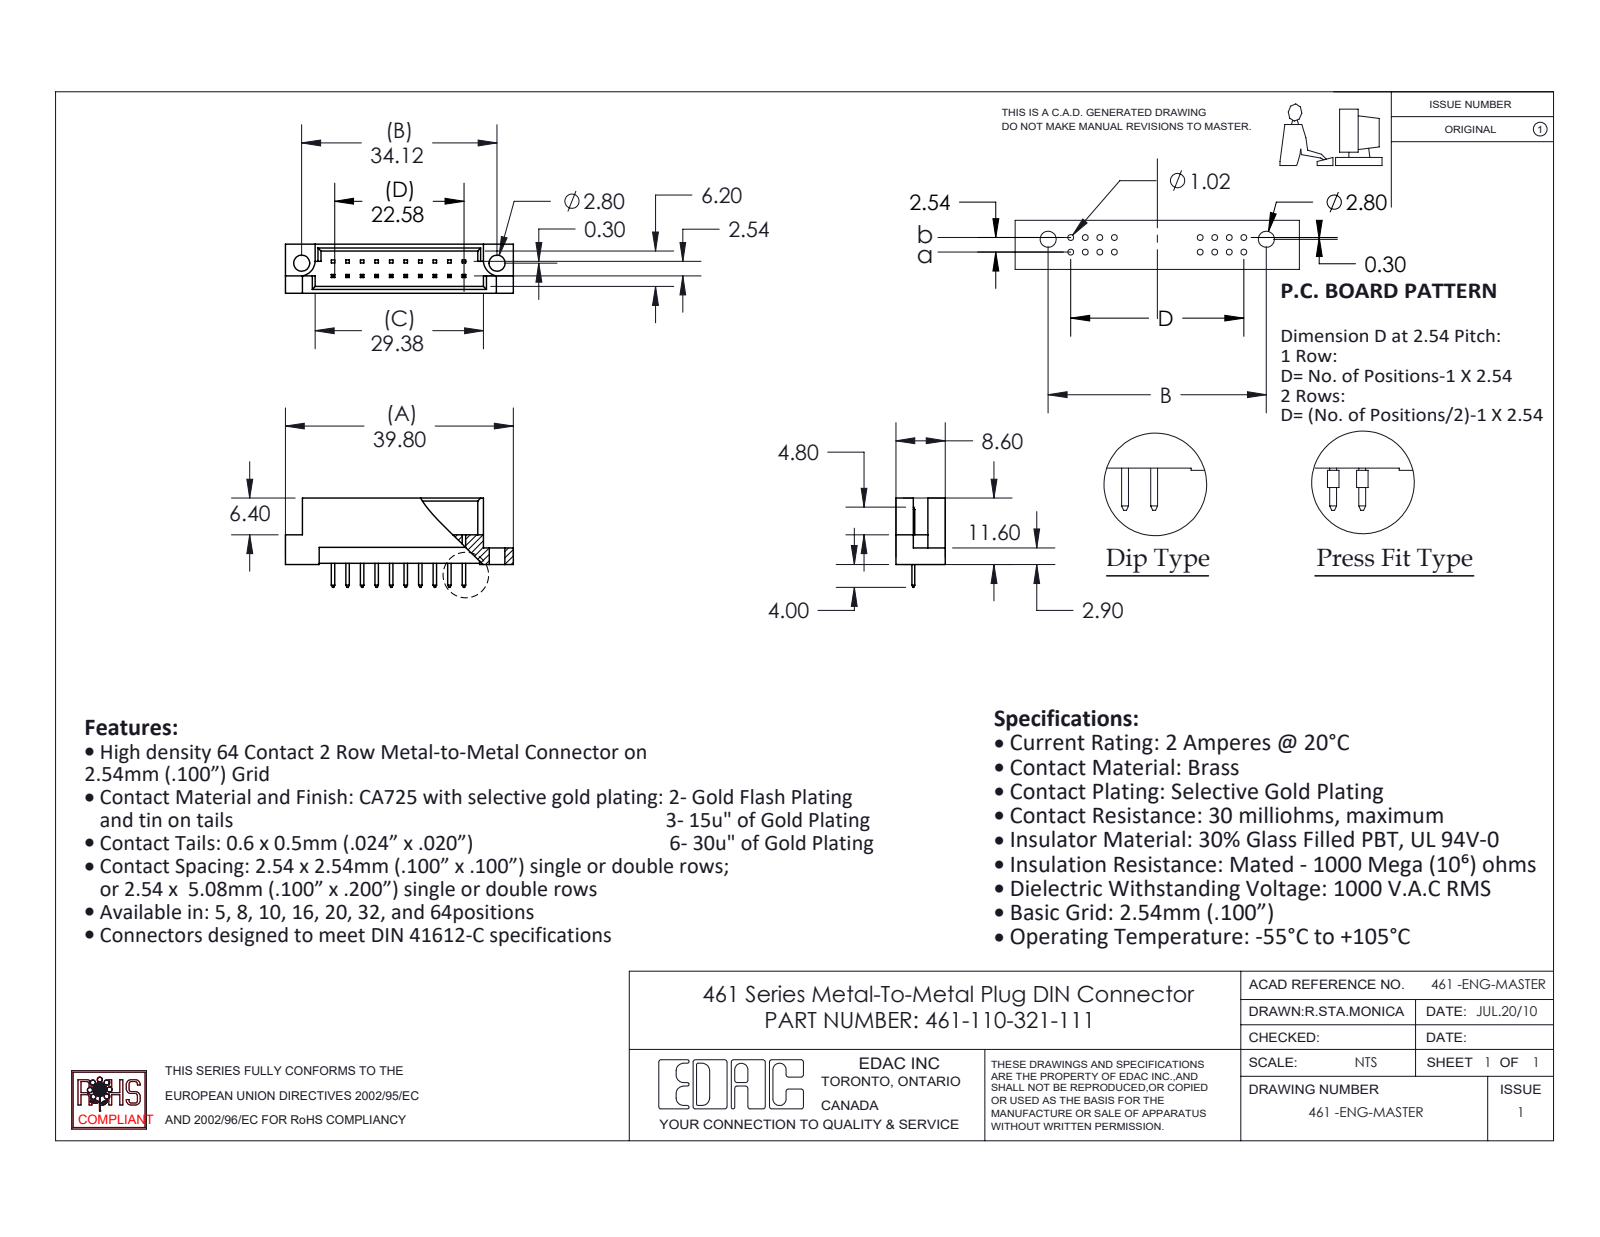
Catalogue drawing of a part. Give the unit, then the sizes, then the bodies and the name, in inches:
Units: inches
Overall size (bounding box): 1.567 × 0.614 × 0.339
Round holes (diameter × count): ⌀0.11 ×2
Partial cylindrical surfaces — rounded edges, fillets, slot ends (radius × count): R0.11 ×2
Main face-to-face distances: 0.047, 0.291, 0.339, 0.244, 0.1, 0.197, 0.129, 0.209, 0.082, 0.162
Hole centre spacings: 1.343
Volume: 0.119 in³ · Surface area: 4.095 in²
Bodies: 11 solids, 268 faces (262 planar, 6 cylindrical, 0 other)
Part name (STEP PRODUCT): 461-290_21; 461 Part_20; 461-110-321-111
STEP written by: SolidWorks 2020 (CONFIG_CONTROL_DESIGN)
